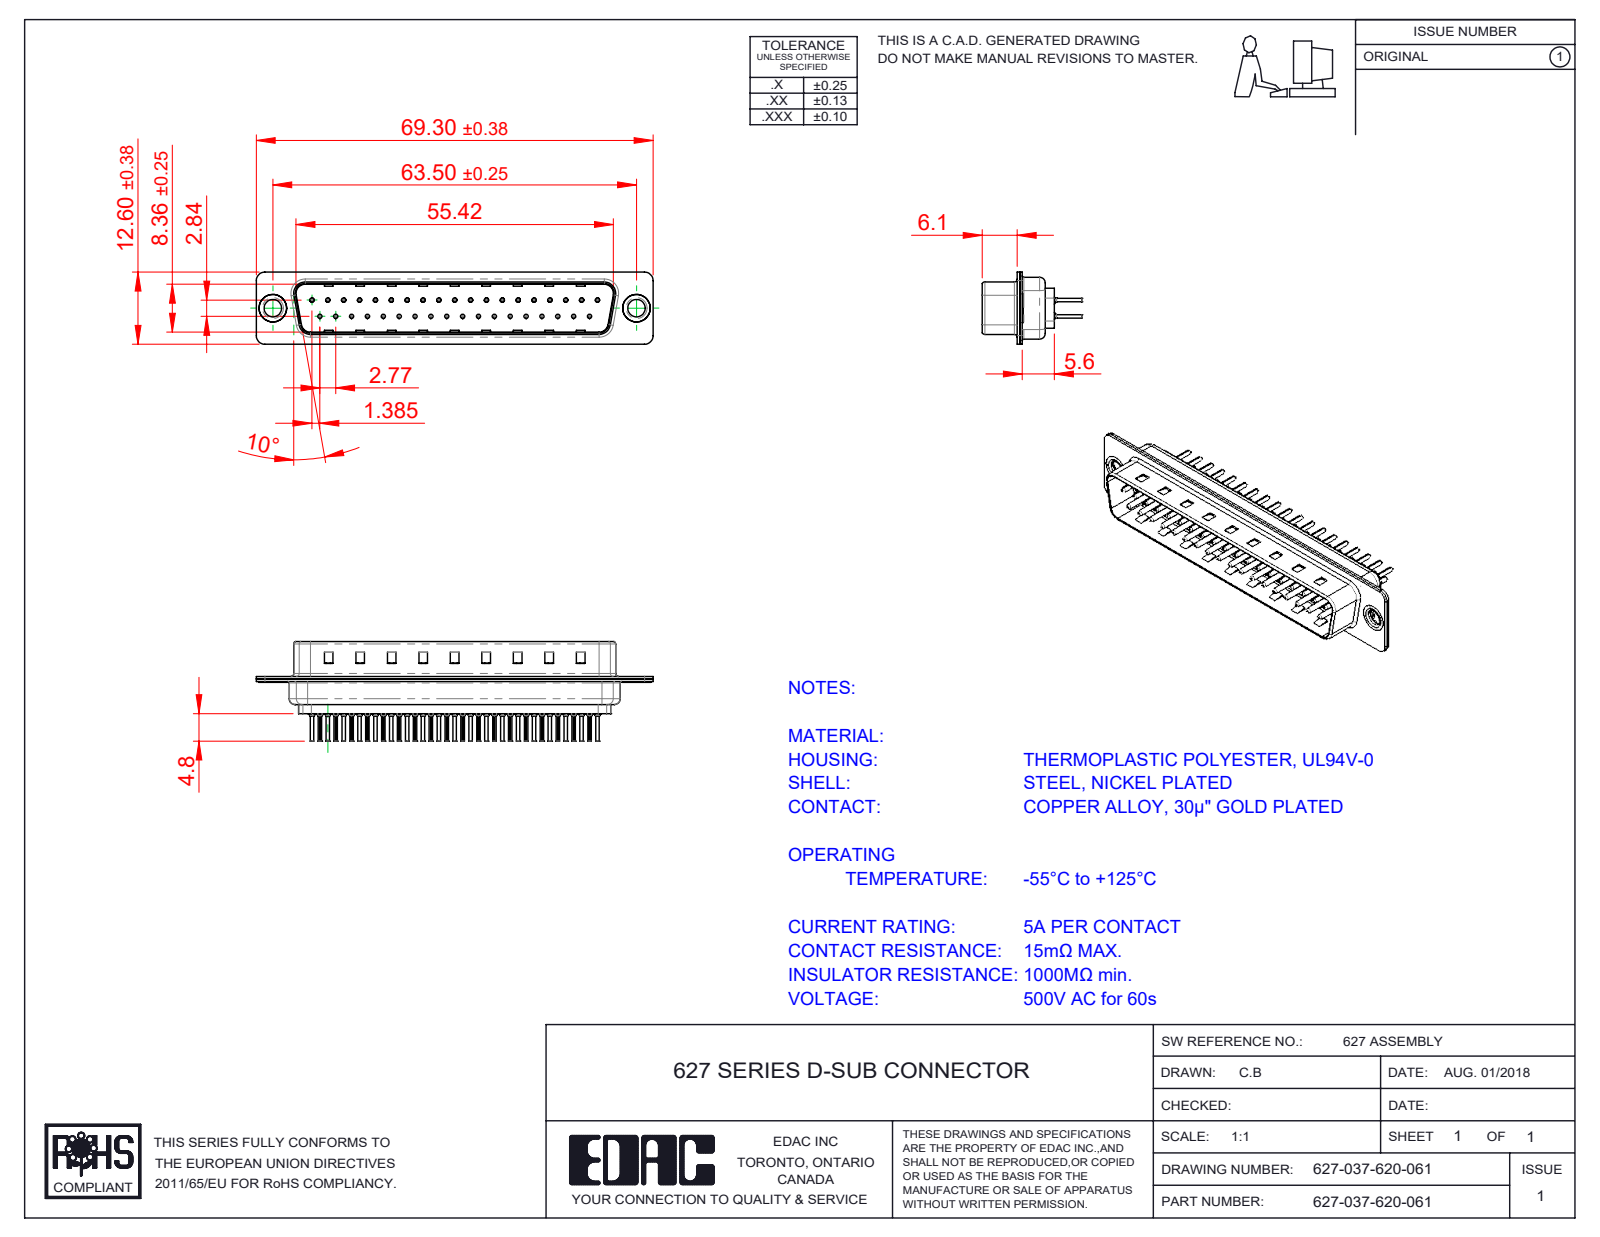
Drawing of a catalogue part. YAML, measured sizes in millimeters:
part_name: "627 Thru Hole Rivet; 627-037-620-061; 627 Housing_37 LP; 627 Contact Row 2_20L (+3 more)"
step_written_by: "SolidWorks 2020 (CONFIG_CONTROL_DESIGN)"
units: millimeters
bodies: {solids: 42, faces: 4012, planar: 1091, cylindrical: 1494, other: 1427}
overall_size: [69.3, 17.3, 12.6]
volume: 3624
surface_area: 10536
round_holes:
  - {diameter: 0.2, count: 37}
  - {diameter: 0.35, count: 37}
  - {diameter: 1.1, count: 37}
  - {diameter: 1.6, count: 37}
  - {diameter: 3.05, count: 2}
  - {diameter: 4, count: 2}
  - {diameter: 4.8, count: 2}
round_bosses_or_shafts:
  - {diameter: 2, count: 37}
  - {diameter: 1.5, count: 37}
  - {diameter: 0.75, count: 37}
  - {diameter: 0.6, count: 37}
  - {diameter: 5, count: 2}
  - {diameter: 4.9, count: 2}
  - {diameter: 3.55, count: 2}
partial_cylinders:
  - {radius: 0.1, count: 74}
  - {radius: 1.5, count: 16}
  - {radius: 2, count: 12}
  - {radius: 0.5, count: 8}
  - {radius: 1.6, count: 8}
  - {radius: 0.25, count: 4}
  - {radius: 0.6, count: 4}
  - {radius: 0.65, count: 4}
face_to_face_distances: [0.4, 0.82, 9.58, 0.45, 8.76, 1.5, 0.9, 1.4, 6.05, 0.5]
hole_center_spacings: [3.16, 2.77, 5.54, 8.31, 5.04, 10.1, 11.08, 12.78]
